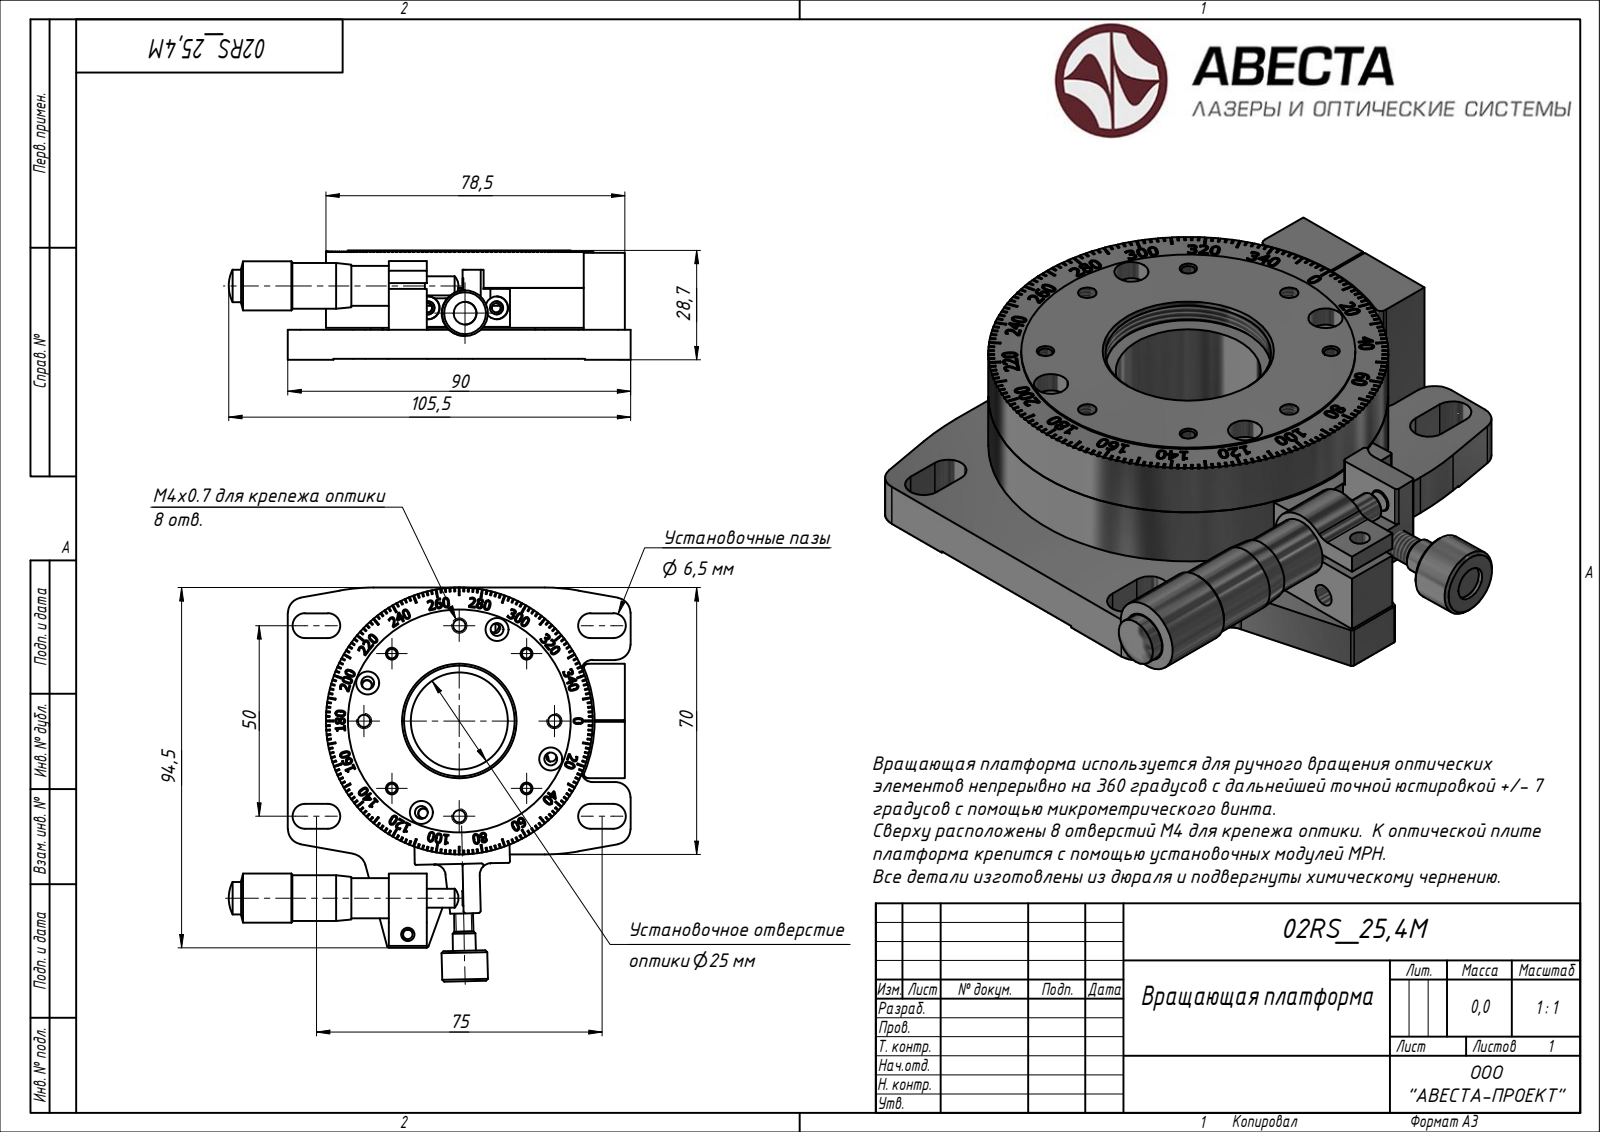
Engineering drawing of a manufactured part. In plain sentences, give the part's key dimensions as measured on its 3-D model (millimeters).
The part is named "Block 01". Its 3-D file was written by "ST-DEVELOPER v15 (AUTOMOTIVE_DESIGN)". It is 28 solids with 2330 faces: 0 planar, 0 cylindrical and 2330 other. Overall it measures 105.5 by 103.41 by 28.7 millimeters. Its volume is 343 cubic millimeters and its surface area 46 344 square millimeters.
